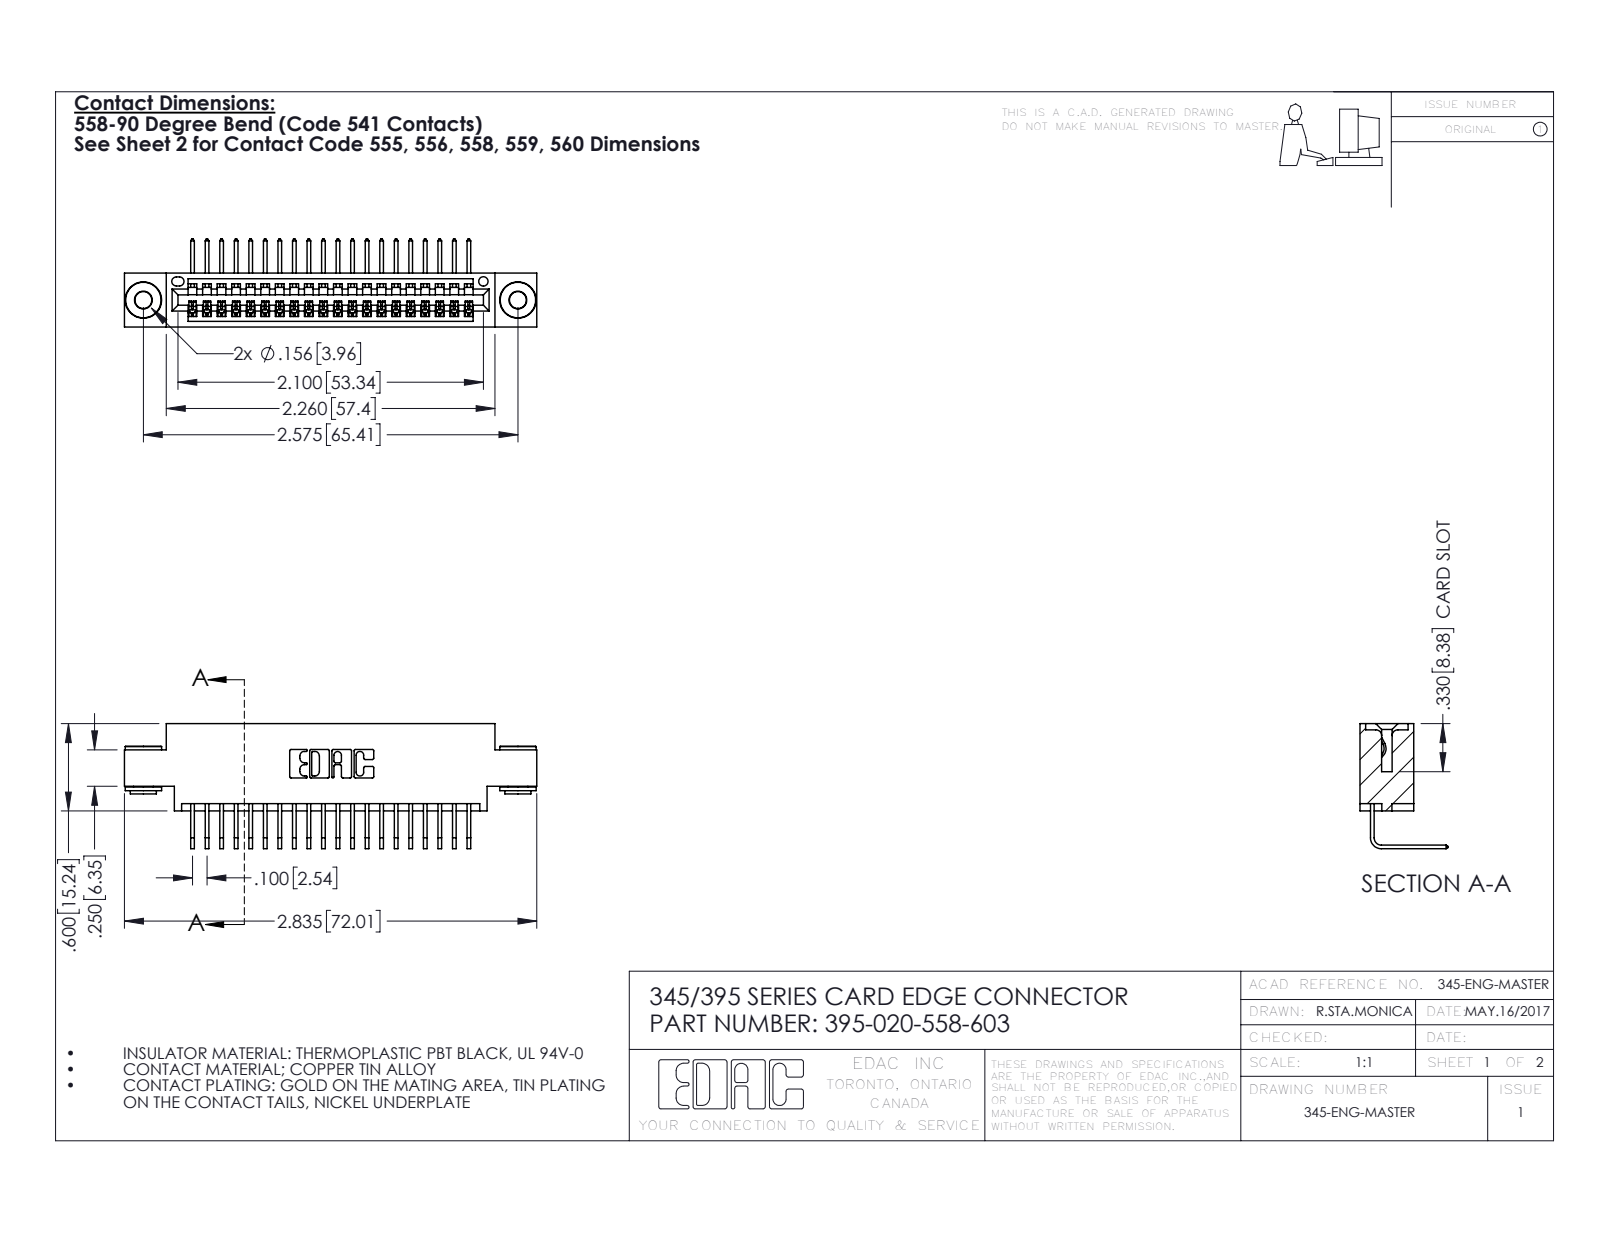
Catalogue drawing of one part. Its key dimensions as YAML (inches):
part_name: "345 Part_0.170 Offset - 0.156 Dia-TH; 395-020-558-603; 345-250-002_345-250-002-102; 345-292-001_558 Tail - 2"
step_written_by: "SolidWorks 2016 (CONFIG_CONTROL_DESIGN)"
units: inches
bodies: {solids: 23, faces: 1368, planar: 934, cylindrical: 426, other: 8}
overall_size: [2.835, 0.859, 0.605]
volume: 0.405
surface_area: 14.33
round_holes:
  - {diameter: 0.116, count: 2}
  - {diameter: 0.156, count: 2}
  - {diameter: 0.064, count: 1}
round_bosses_or_shafts:
  - {diameter: 0.25, count: 2}
  - {diameter: 0.18, count: 2}
  - {diameter: 0.136, count: 2}
partial_cylinders:
  - {radius: 0.006, count: 40}
  - {radius: 0.01, count: 22}
  - {radius: 0.007, count: 6}
  - {radius: 0.031, count: 6}
  - {radius: 0.026, count: 3}
  - {radius: 0.031, count: 2}
  - {radius: 0.04, count: 2}
  - {radius: 0.014, count: 1}
face_to_face_distances: [0.072, 0.298, 0.37, 0.2, 0.098, 0.272, 0.025, 0.225, 0.175, 0.1]
hole_center_spacings: [0.27, 2.341, 2.575]
